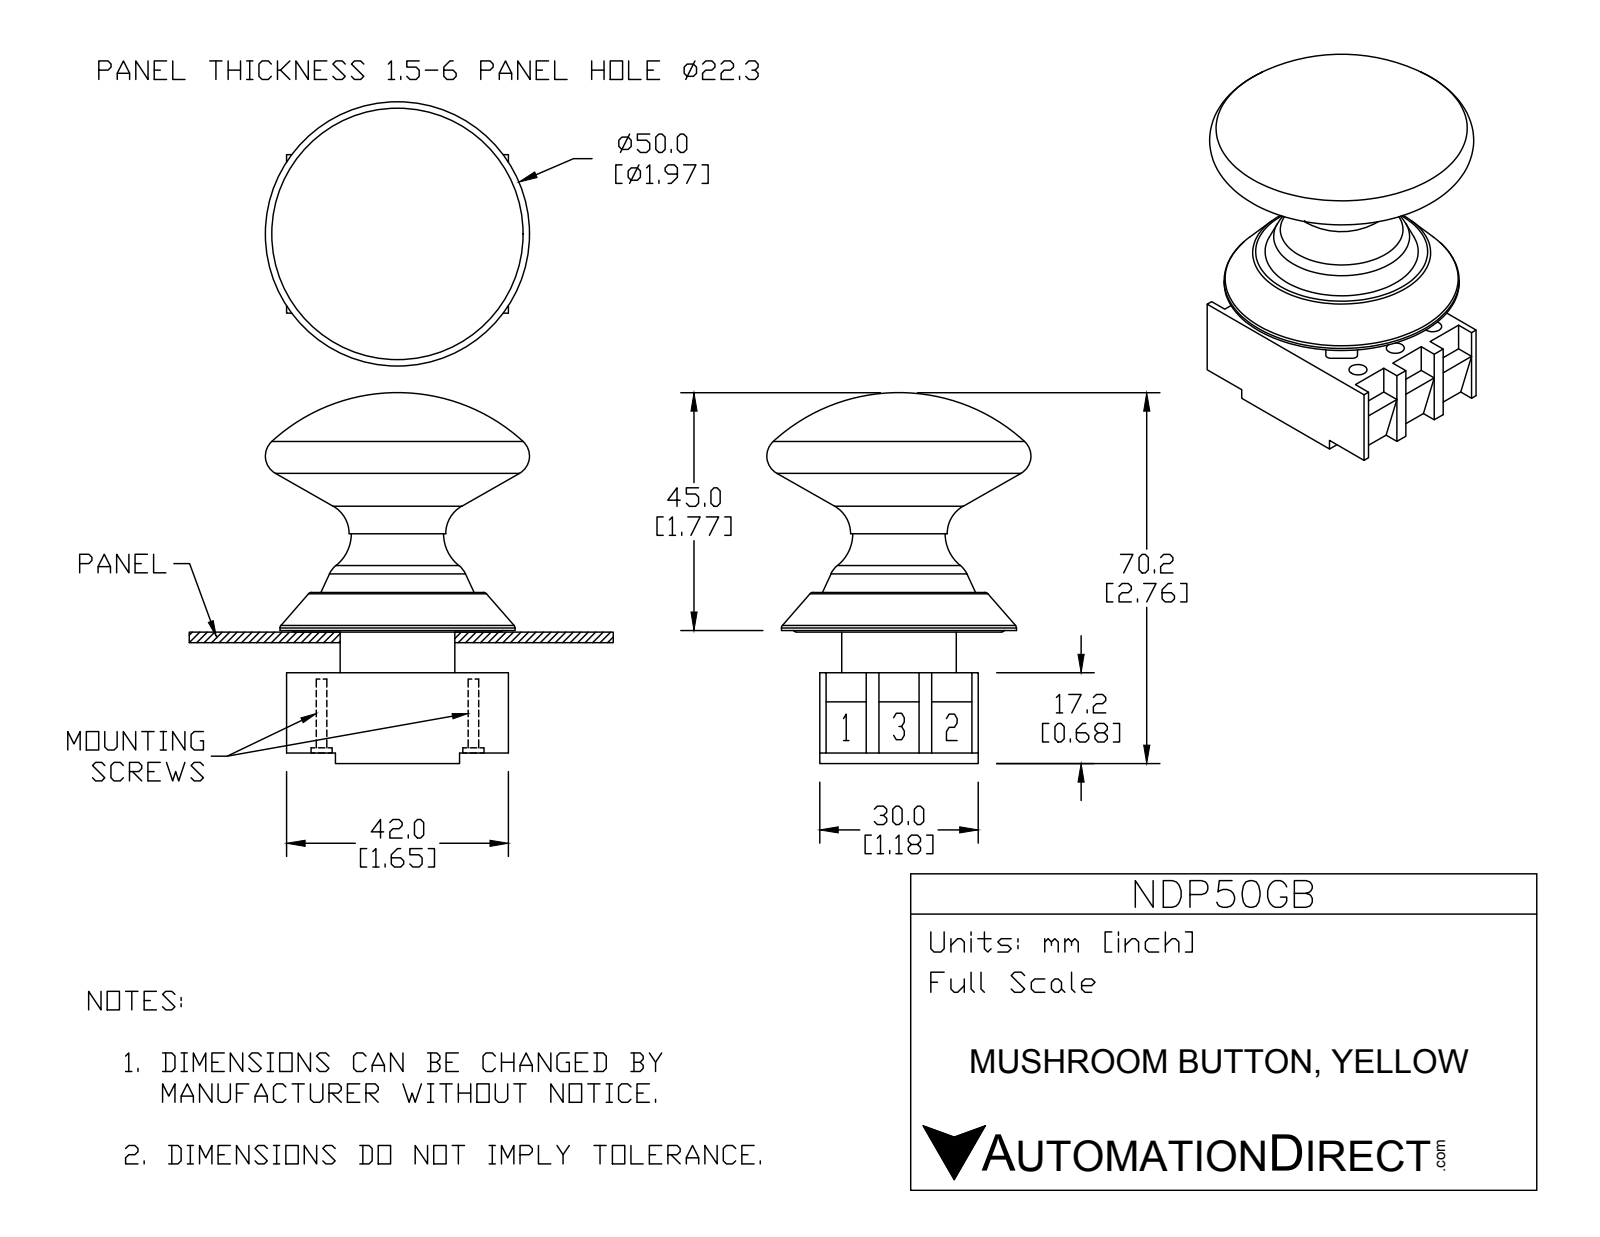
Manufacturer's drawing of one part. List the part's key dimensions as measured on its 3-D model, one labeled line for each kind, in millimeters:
Part name (STEP PRODUCT): NDP50GB
STEP written by: SolidWorks 2015 (AUTOMOTIVE_DESIGN)
Units: millimetres
Bodies: 7 solids, 222 faces (126 planar, 63 cylindrical, 33 other)
Overall size (bounding box): 70.2 × 50 × 50
Volume: 55 695 mm³ · Surface area: 21 605 mm²
Round holes (diameter × count): ⌀3.4 ×6, ⌀5 ×6, ⌀12.5 ×1
Round bosses / shafts (diameter × count): ⌀4.6 ×2, ⌀4 ×2, ⌀44.5 ×1, ⌀21.7 ×1
Partial cylindrical surfaces — rounded edges, fillets, slot ends (radius × count): R1 ×8, R8.7 ×5, R11 ×1
Main face-to-face distances: 7.2, 15.2, 30, 8, 7.5, 7.7, 22.9, 10, 23.2, 30.4
Hole centre spacings: 10, 17.52, 30.45, 28.76, 14.38, 20, 35.03
